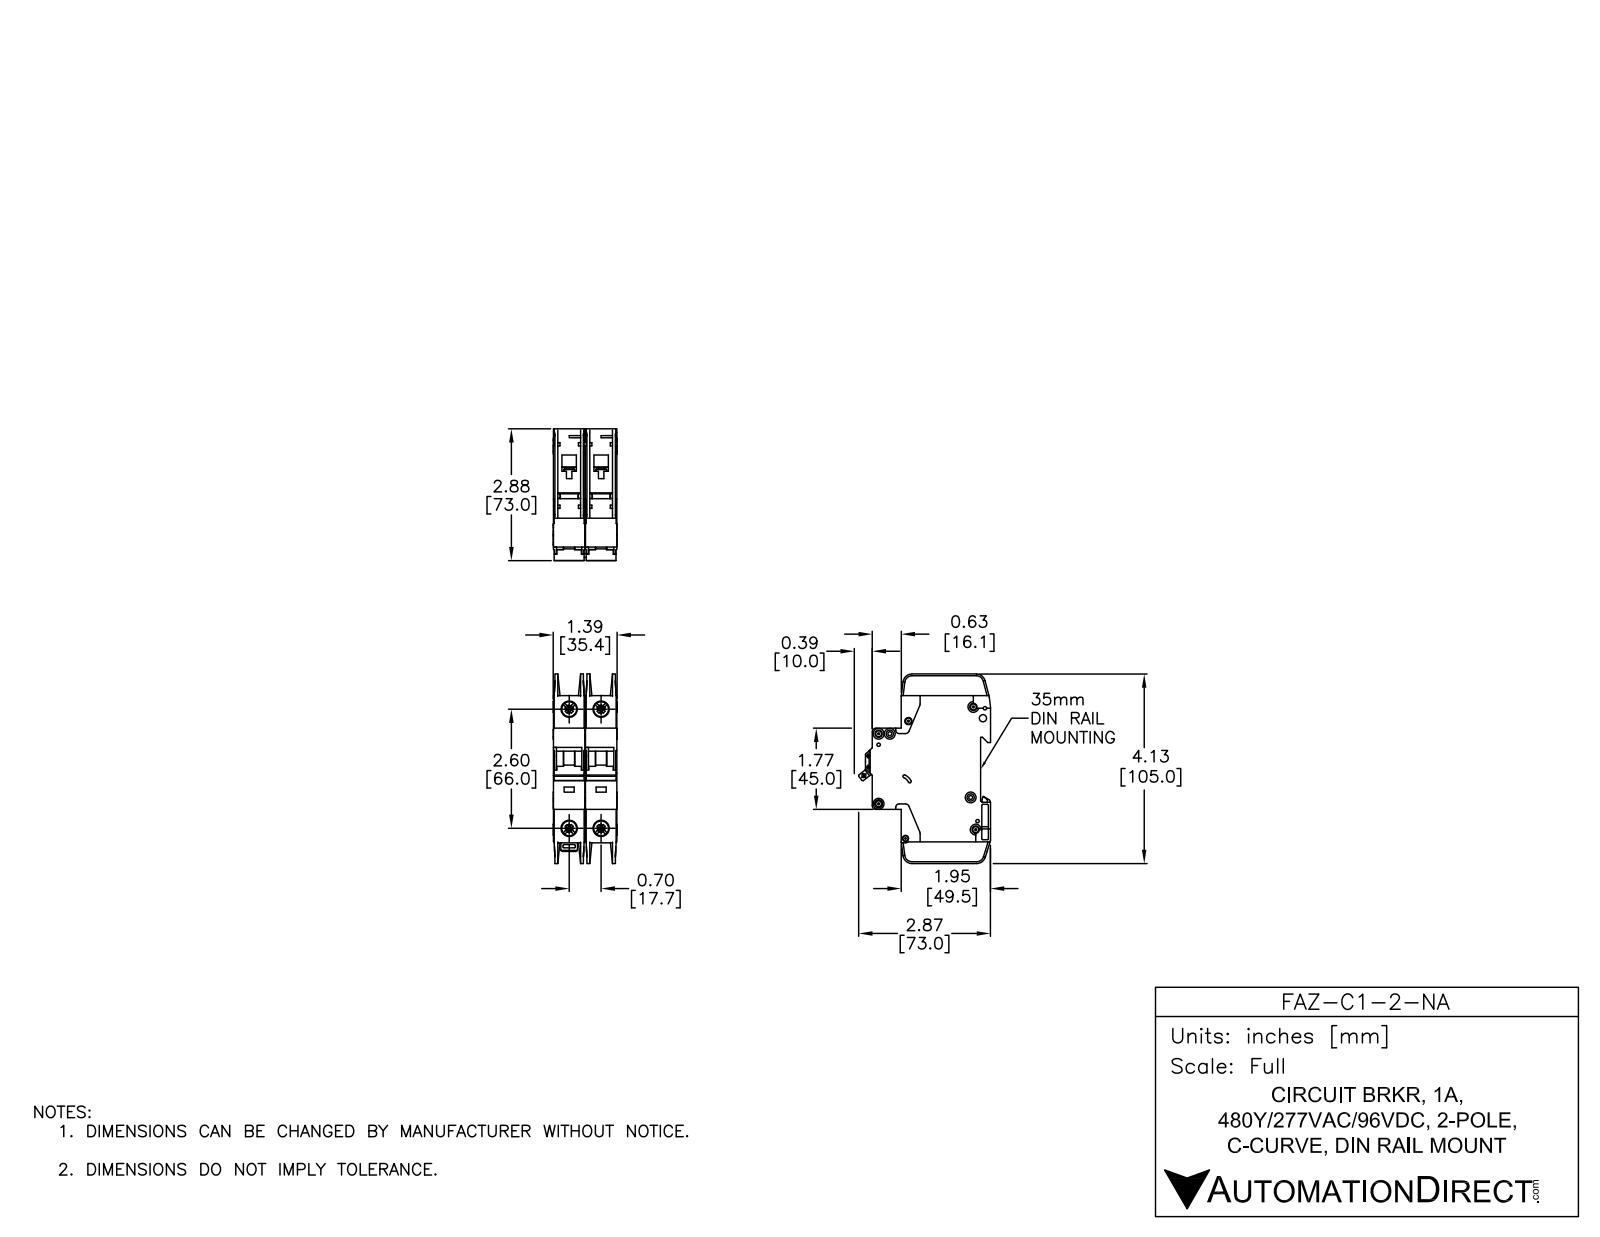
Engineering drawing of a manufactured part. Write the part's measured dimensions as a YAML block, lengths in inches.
part_name: "FAZ-C1-2-NA"
step_written_by: "SolidWorks 2014 (AUTOMOTIVE_DESIGN)"
units: inches
bodies: {solids: 6, faces: 1568, planar: 818, cylindrical: 526, other: 224}
overall_size: [4.134, 2.876, 1.394]
volume: 9.482
surface_area: 76.69
round_holes:
  - {diameter: 0.142, count: 7}
  - {diameter: 0.281, count: 4}
  - {diameter: 0.323, count: 4}
  - {diameter: 0.043, count: 2}
  - {diameter: 0.059, count: 2}
  - {diameter: 0.157, count: 2}
  - {diameter: 0.075, count: 1}
  - {diameter: 0.085, count: 1}
  - {diameter: 0.087, count: 1}
  - {diameter: 0.1, count: 1}
  - {diameter: 0.13, count: 1}
  - {diameter: 0.134, count: 1}
round_bosses_or_shafts:
  - {diameter: 0.236, count: 7}
  - {diameter: 0.098, count: 2}
partial_cylinders:
  - {radius: 0.01, count: 47}
  - {radius: 0.02, count: 24}
  - {radius: 0.039, count: 18}
  - {radius: 0.079, count: 12}
  - {radius: 0.197, count: 5}
  - {radius: 0.071, count: 4}
  - {radius: 0.157, count: 4}
  - {radius: 0.008, count: 2}
face_to_face_distances: [0.697, 0.689, 0.028, 0.593, 0.096, 0.069, 0.62, 0.524, 1.386, 0.669]
hole_center_spacings: [0.244, 0.697, 2.598, 2.69, 0.204, 0.24, 0.322, 0.337]
